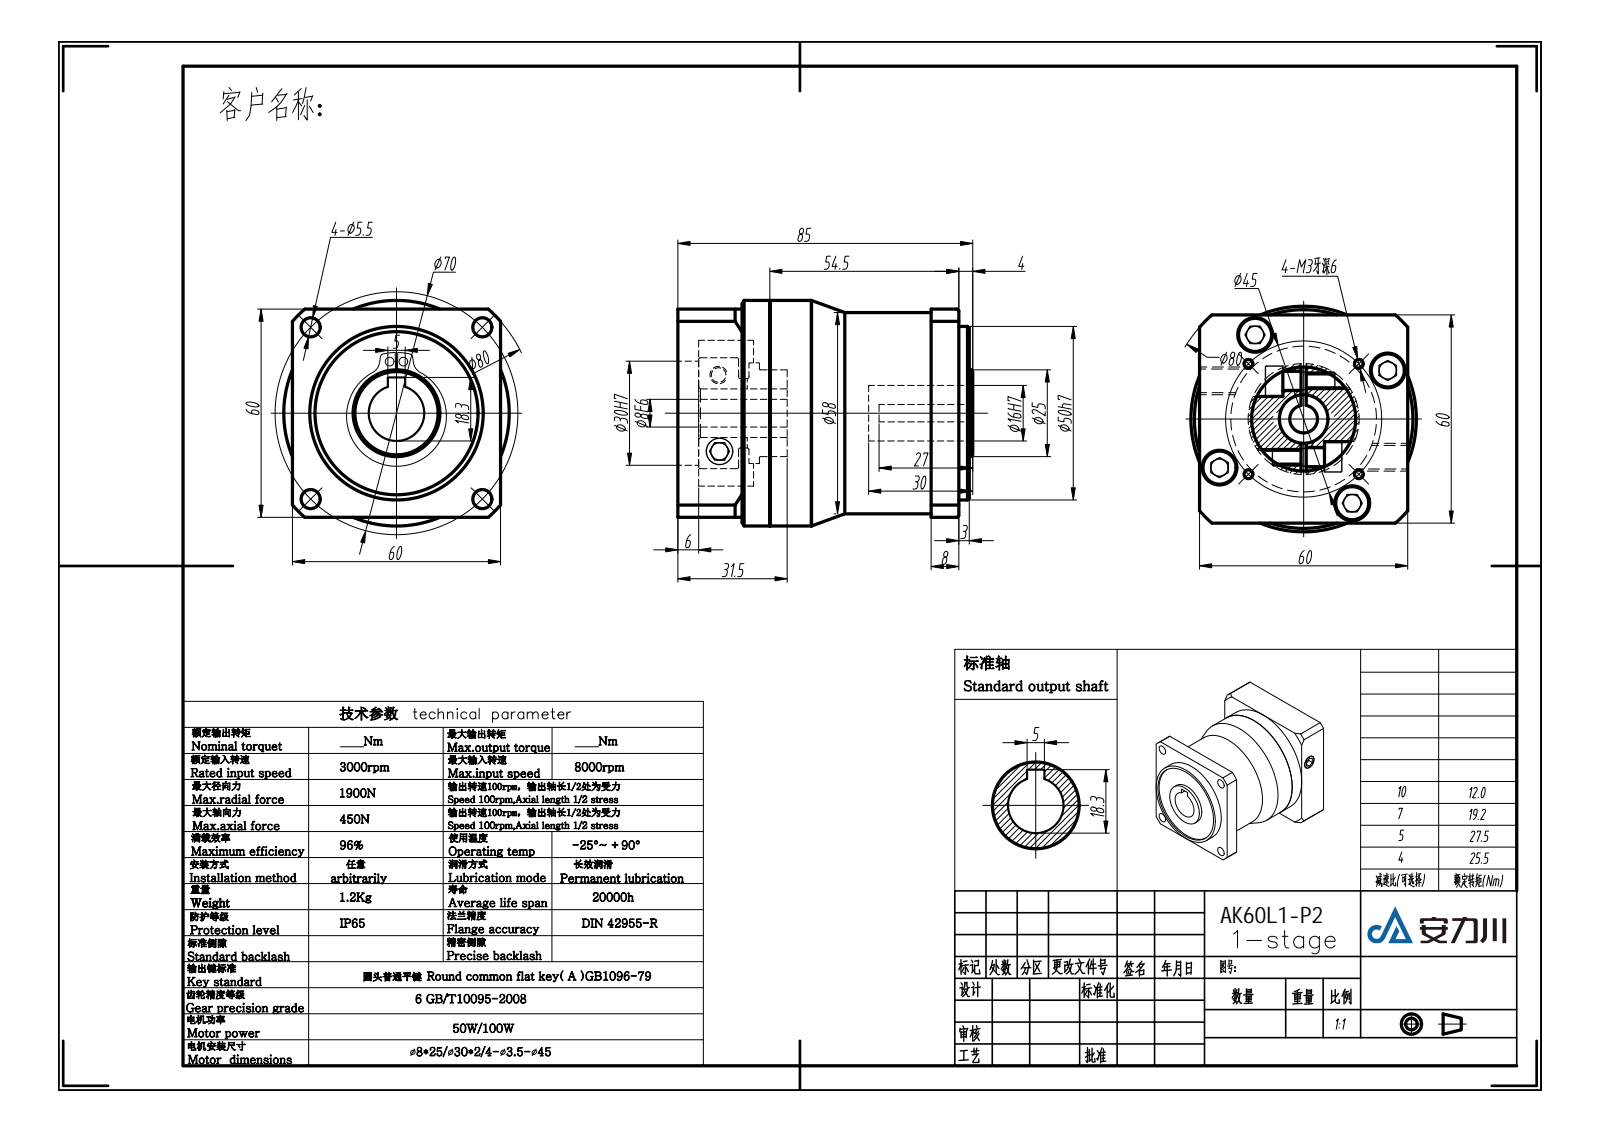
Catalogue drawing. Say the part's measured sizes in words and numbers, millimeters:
The part is named "VGK60单级模型（8-25 30-3 4-3.5-45）". Its 3-D file was written by "SolidWorks 2016 (AUTOMOTIVE_DESIGN)". It is 3 solids with 203 faces: 99 planar, 82 cylindrical and 22 other. Overall it measures 85 by 65 by 65 millimeters. Its volume is 233 563 cubic millimeters and its surface area 46 140 square millimeters. Round holes: 4 of diameter 2.5, 4 of diameter 5.5, 4 of diameter 10, 3 of diameter 8, 1 of diameter 14, 1 of diameter 16, 1 of diameter 30, 1 of diameter 42, 1 of diameter 47. Round bosses or shafts: 4 of diameter 8.5, 2 of diameter 7.6, 1 of diameter 65, 1 of diameter 58, 1 of diameter 50, 1 of diameter 32, 1 of diameter 25, 1 of diameter 20. Partial cylindrical surfaces (rounded edges, fillets, slot ends): 1 of radius 40. The main face-to-face distances are 60, 26.5, 20.5, 6, 2, 54.5, 62.5, 81, 8, 75. The hole center spacings are 41.61, 8.56, 10.76, 12.5, 22.5, 28, 31.05, 31.82.
